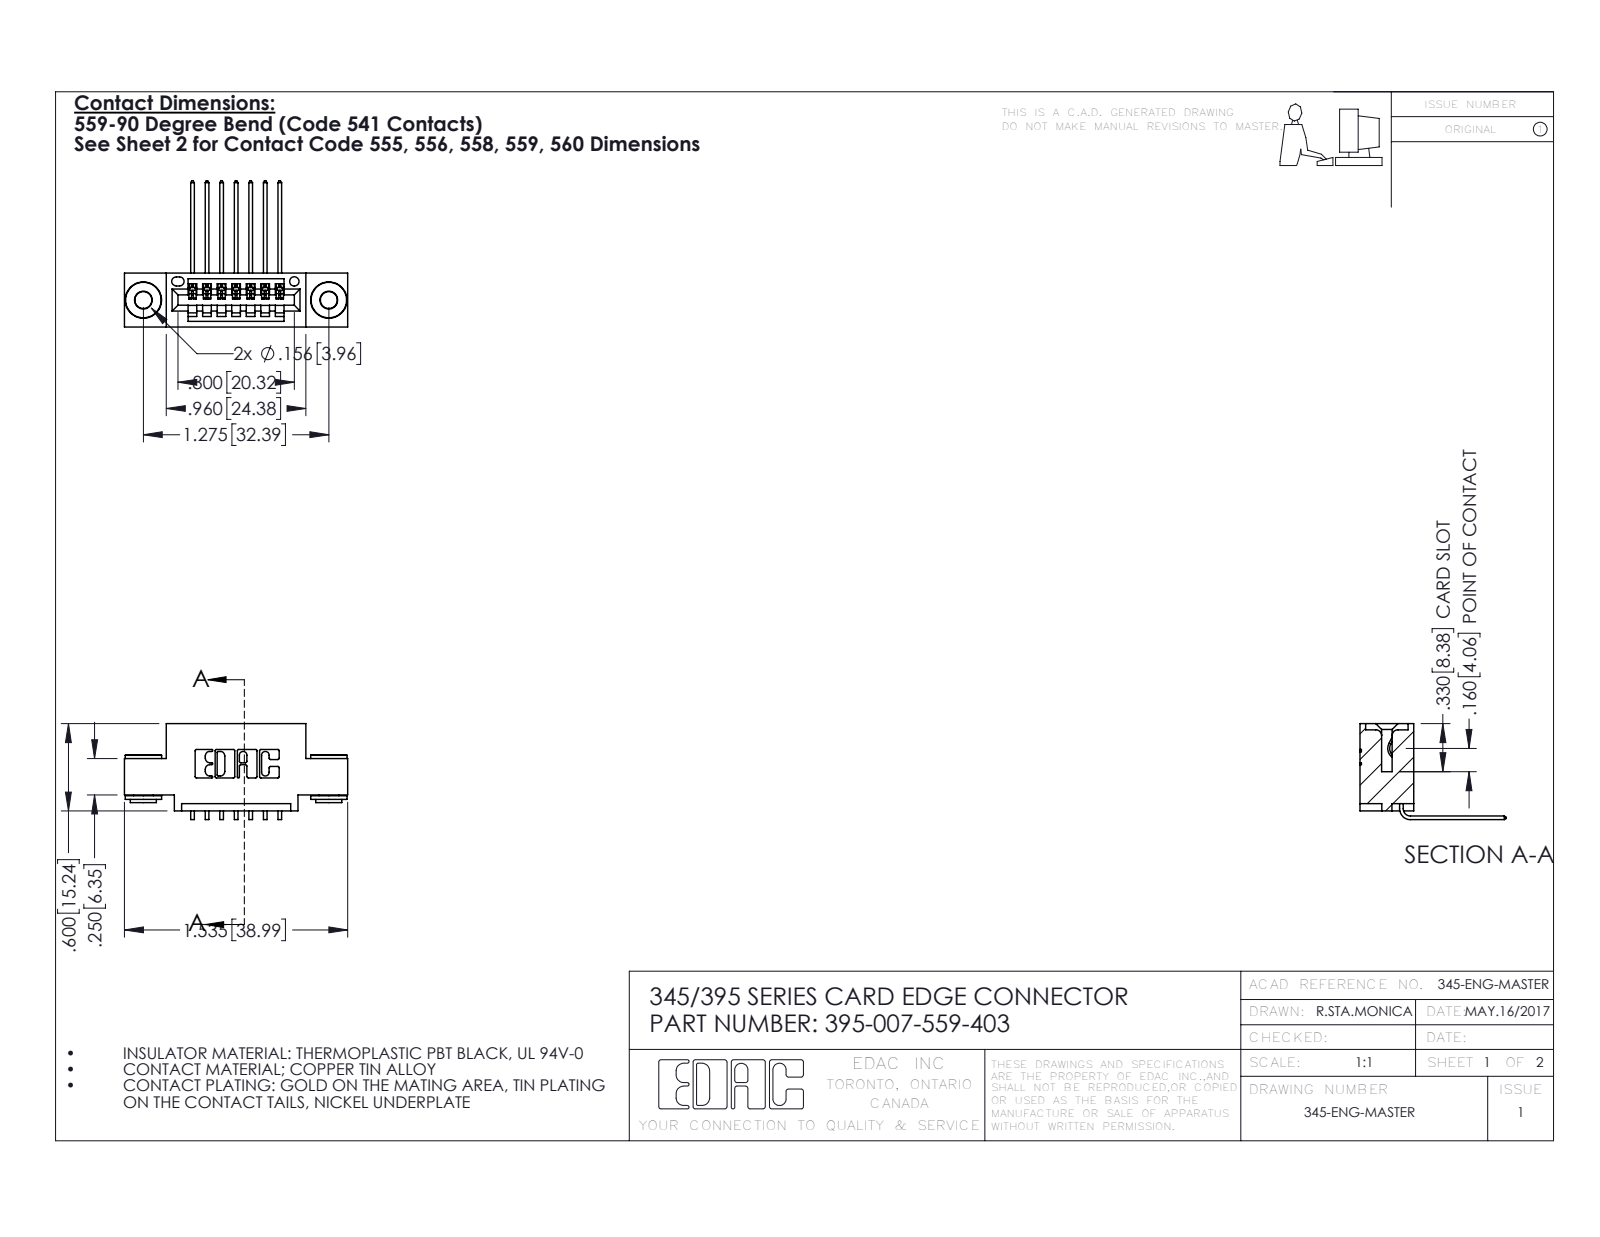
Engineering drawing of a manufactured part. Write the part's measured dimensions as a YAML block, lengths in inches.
part_name: "345 Part_0.110 Offset - 0.156 Dia-TH; 345-292-001_558 559 Tail - 1; 395-007-559-403; 345-250-002_345-250-002-102"
step_written_by: "SolidWorks 2016 (CONFIG_CONTROL_DESIGN)"
units: inches
bodies: {solids: 10, faces: 588, planar: 388, cylindrical: 192, other: 8}
overall_size: [1.535, 1.005, 0.659]
volume: 0.207
surface_area: 6.909
round_holes:
  - {diameter: 0.116, count: 2}
  - {diameter: 0.156, count: 2}
  - {diameter: 0.064, count: 1}
round_bosses_or_shafts:
  - {diameter: 0.25, count: 2}
  - {diameter: 0.18, count: 2}
  - {diameter: 0.136, count: 2}
partial_cylinders:
  - {radius: 0.01, count: 22}
  - {radius: 0.006, count: 14}
  - {radius: 0.007, count: 6}
  - {radius: 0.031, count: 6}
  - {radius: 0.026, count: 3}
  - {radius: 0.031, count: 2}
  - {radius: 0.04, count: 2}
  - {radius: 0.014, count: 1}
face_to_face_distances: [0.2, 0.37, 0.1, 0.072, 0.298, 0.025, 0.3, 0.16, 0.06, 0.25]
hole_center_spacings: [0.27, 1.045, 1.275]
